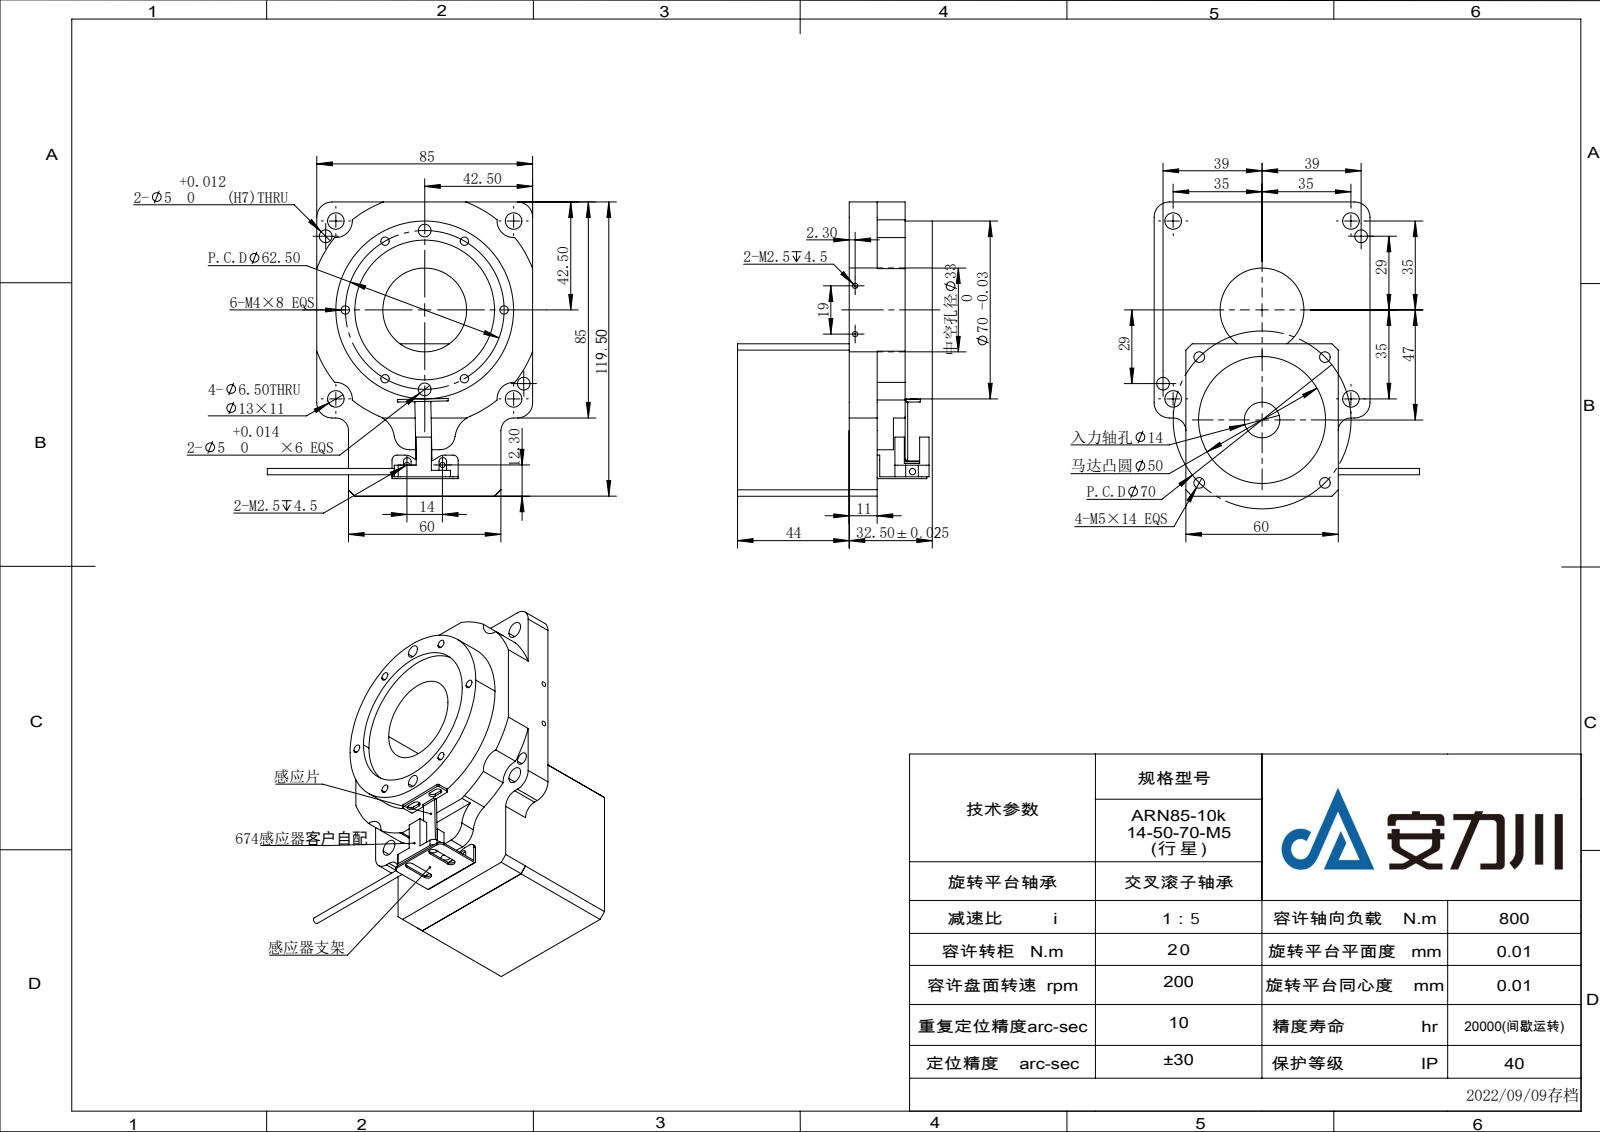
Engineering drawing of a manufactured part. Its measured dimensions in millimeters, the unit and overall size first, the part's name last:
Units: millimetres
Overall size (bounding box): 119.5 × 104.5 × 76.5
Round holes (diameter × count): ⌀2.05 ×6, ⌀3.3 ×6, ⌀4.2 ×4, ⌀5 ×4, ⌀6.5 ×4, ⌀3.5 ×2, ⌀14 ×1, ⌀33 ×1, ⌀50 ×1, ⌀55 ×1
Round bosses / shafts (diameter × count): ⌀70 ×1, ⌀2.5 ×1
Partial cylindrical surfaces — rounded edges, fillets, slot ends (radius × count): R0.5 ×9, R1.5 ×8, R2 ×6, R6 ×6, R1.65 ×4, R5 ×4, R6.5 ×4, R1 ×2
Main face-to-face distances: 11, 60, 44, 55, 22, 12.5, 72.5, 33, 66, 73.7
Hole centre spacings: 31.25, 35.2, 49.5, 74.93, 70, 54.13, 35, 44.19
Volume: 311 558 mm³ · Surface area: 49 738 mm²
Bodies: 4 solids, 278 faces (112 planar, 126 cylindrical, 40 other)
Part name (STEP PRODUCT): KTN85-5K-14-50-70-M5配行星; 感应器支架; SX674; 感应片1
STEP written by: SolidWorks 2020 (AUTOMOTIVE_DESIGN)
